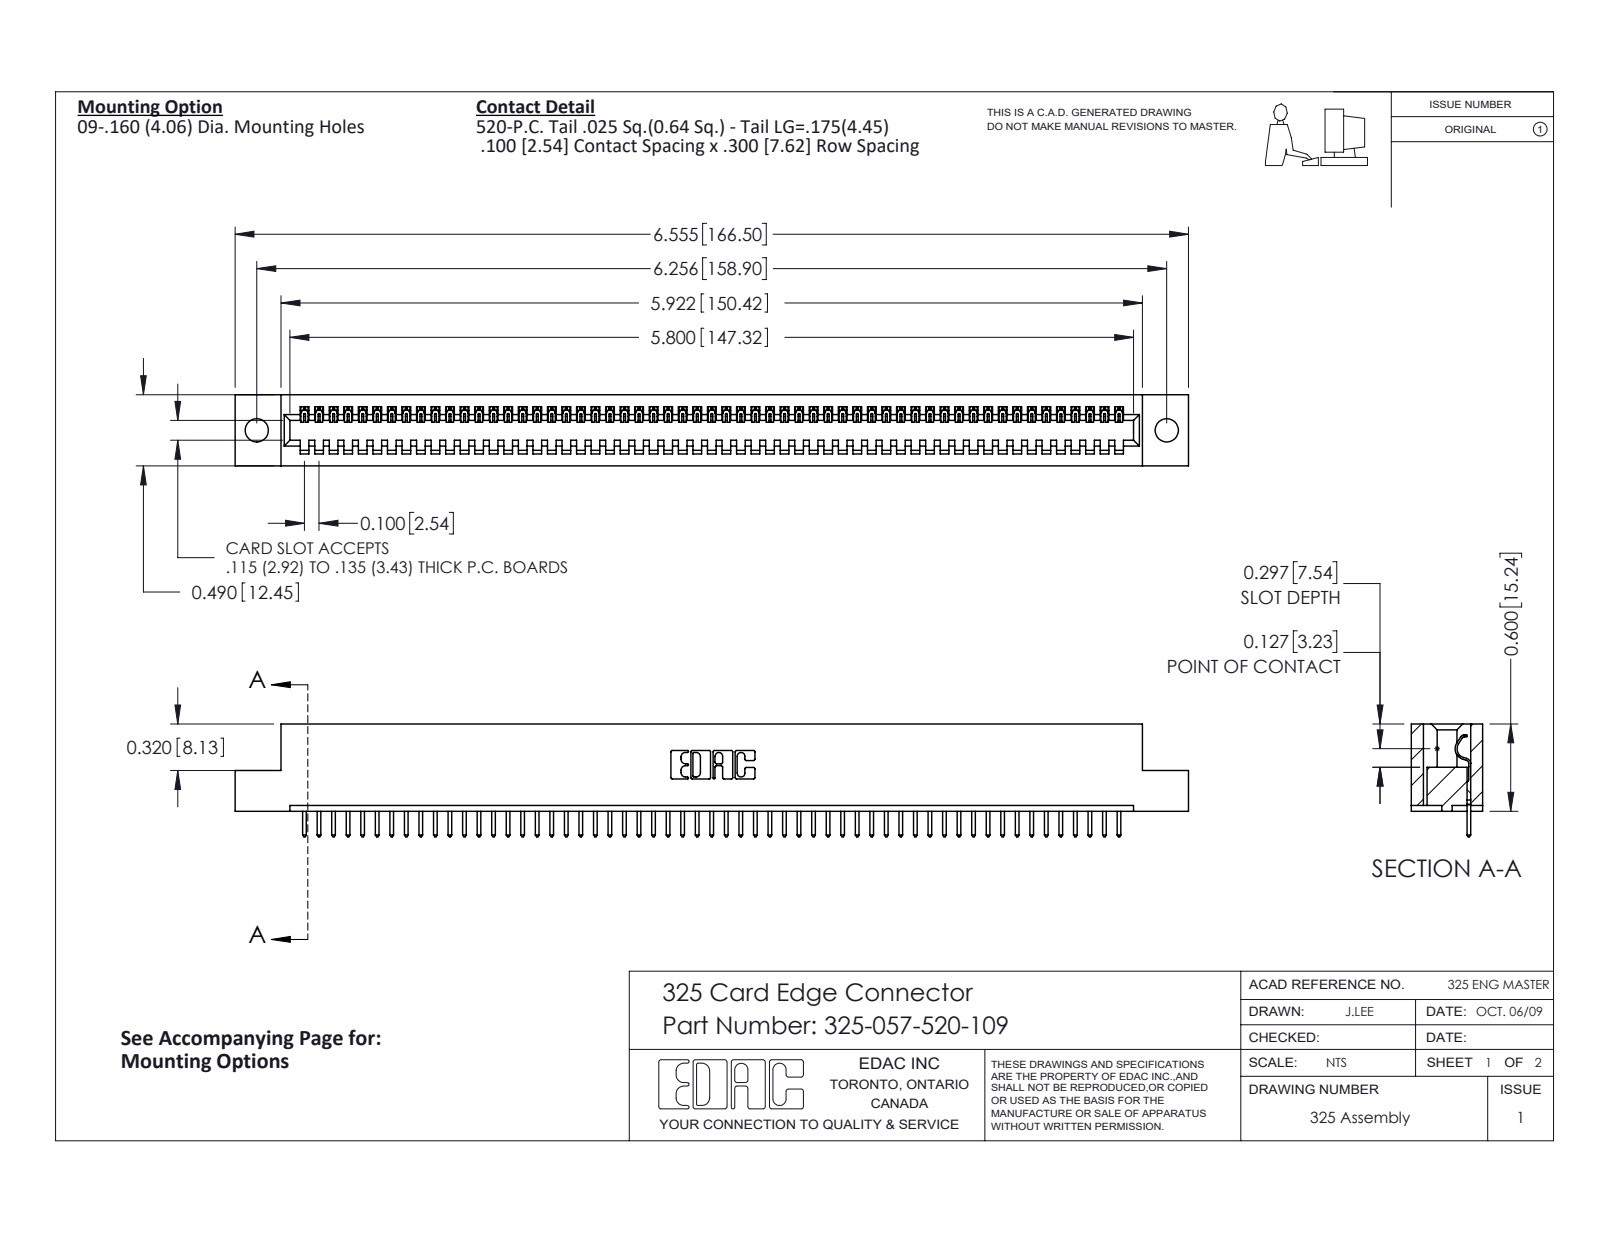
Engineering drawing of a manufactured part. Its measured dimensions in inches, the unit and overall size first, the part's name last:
Units: inches
Overall size (bounding box): 6.555 × 0.775 × 0.49
Round holes (diameter × count): ⌀0.16 ×2
Partial cylindrical surfaces — rounded edges, fillets, slot ends (radius × count): R0.006 ×114, R0.01 ×114, R0.01 ×22, R0.007 ×6, R0.031 ×6, R0.026 ×3, R0.014 ×1, R0.022 ×1
Main face-to-face distances: 0.083, 0.407, 0.49, 0.3, 0.107, 0.383, 0.025, 0.325, 0.56, 0.263
Hole centre spacings: 6.256
Volume: 1.274 in³ · Surface area: 34.66 in²
Bodies: 58 solids, 3420 faces (2464 planar, 956 cylindrical, 0 other)
Part name (STEP PRODUCT): 325-057-520-109; 325-292-001_325-293-120; 325 Part_.160 TH
STEP written by: SolidWorks 2016 (CONFIG_CONTROL_DESIGN)
